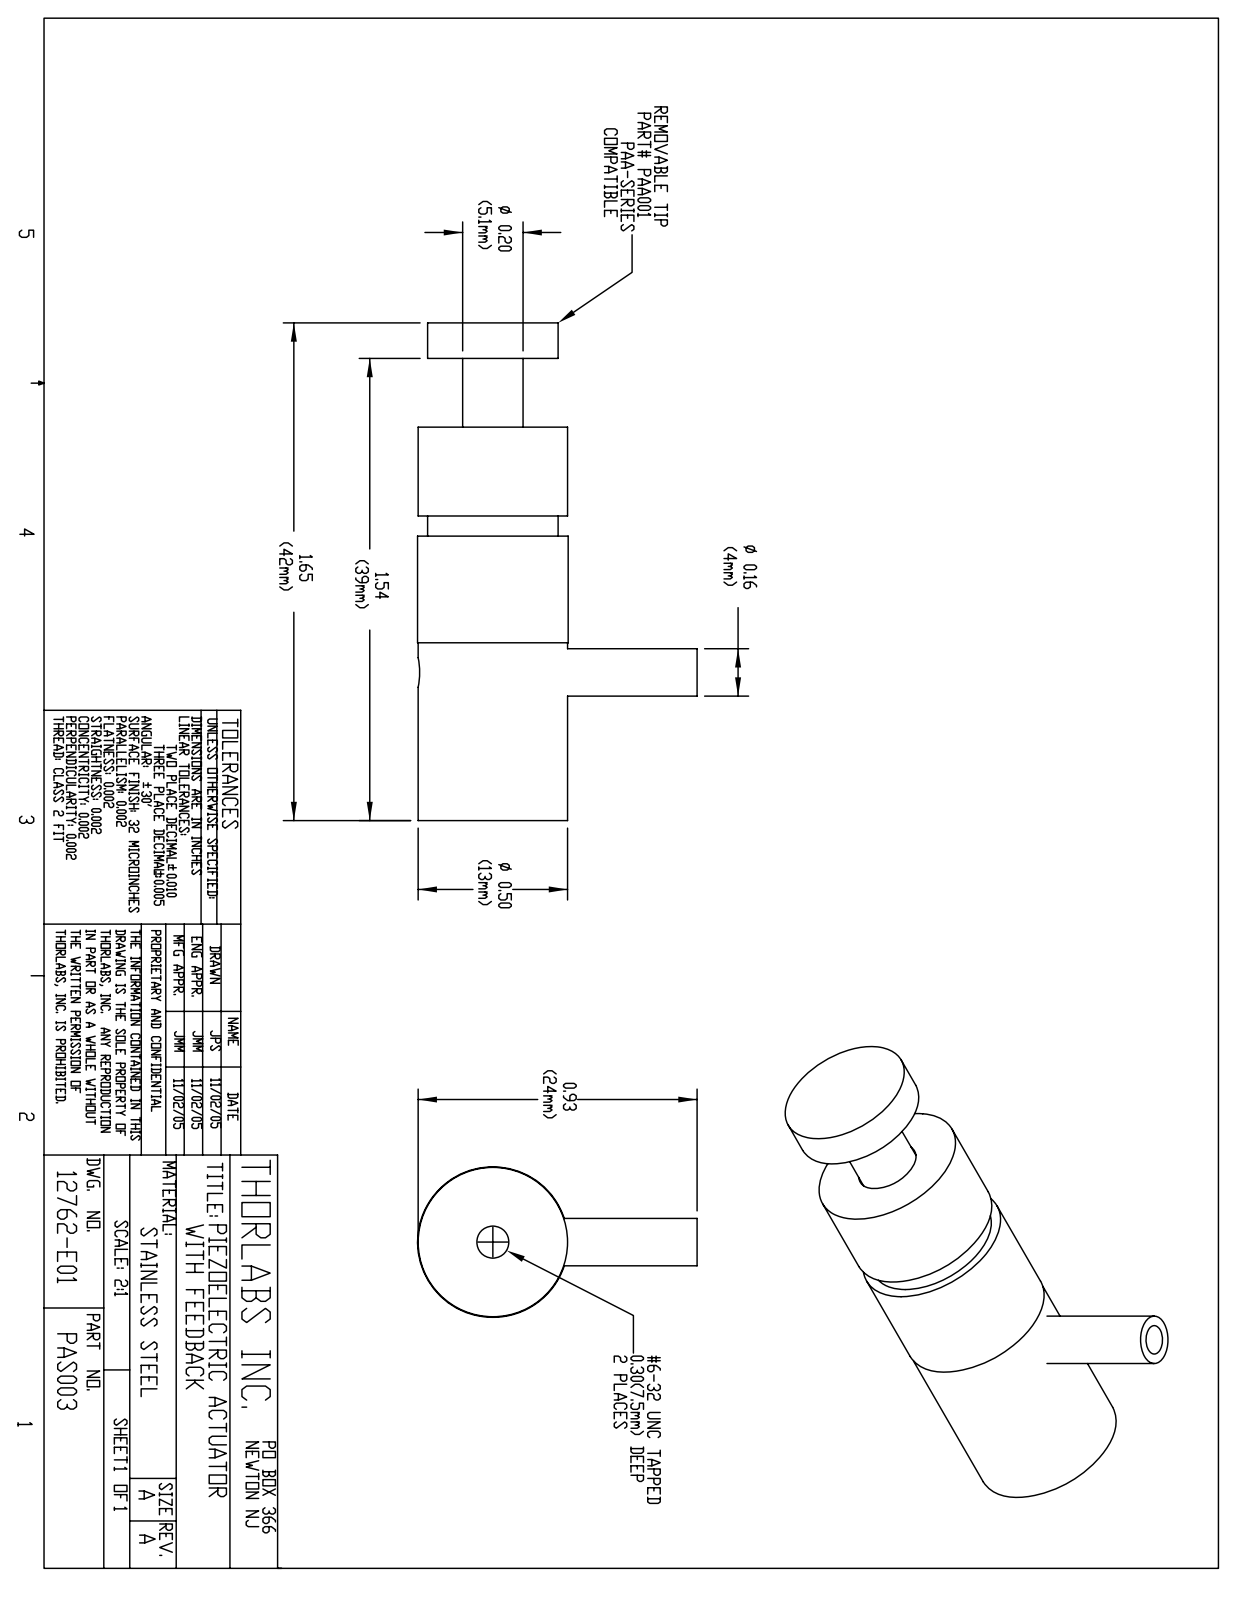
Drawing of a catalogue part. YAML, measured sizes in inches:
part_name: "12762-E0W"
step_written_by: "SolidWorks 2007 (AUTOMOTIVE_DESIGN)"
units: inches
bodies: {solids: 0, faces: 39, planar: 11, cylindrical: 28, other: 0}
overall_size: [1.654, 0.928, 0.5]
round_holes:
  - {diameter: 0.098, count: 2}
  - {diameter: 0.094, count: 1}
  - {diameter: 0.107, count: 1}
  - {diameter: 0.209, count: 1}
  - {diameter: 0.376, count: 1}
  - {diameter: 0.449, count: 1}
round_bosses_or_shafts:
  - {diameter: 0.5, count: 1}
  - {diameter: 0.496, count: 1}
  - {diameter: 0.433, count: 1}
  - {diameter: 0.201, count: 1}
  - {diameter: 0.157, count: 1}
face_to_face_distances: [1.307, 0.346, 1.654, 0.118, 0.228, 1.535, 1.26, 1.142, 0.913, 0.394]
